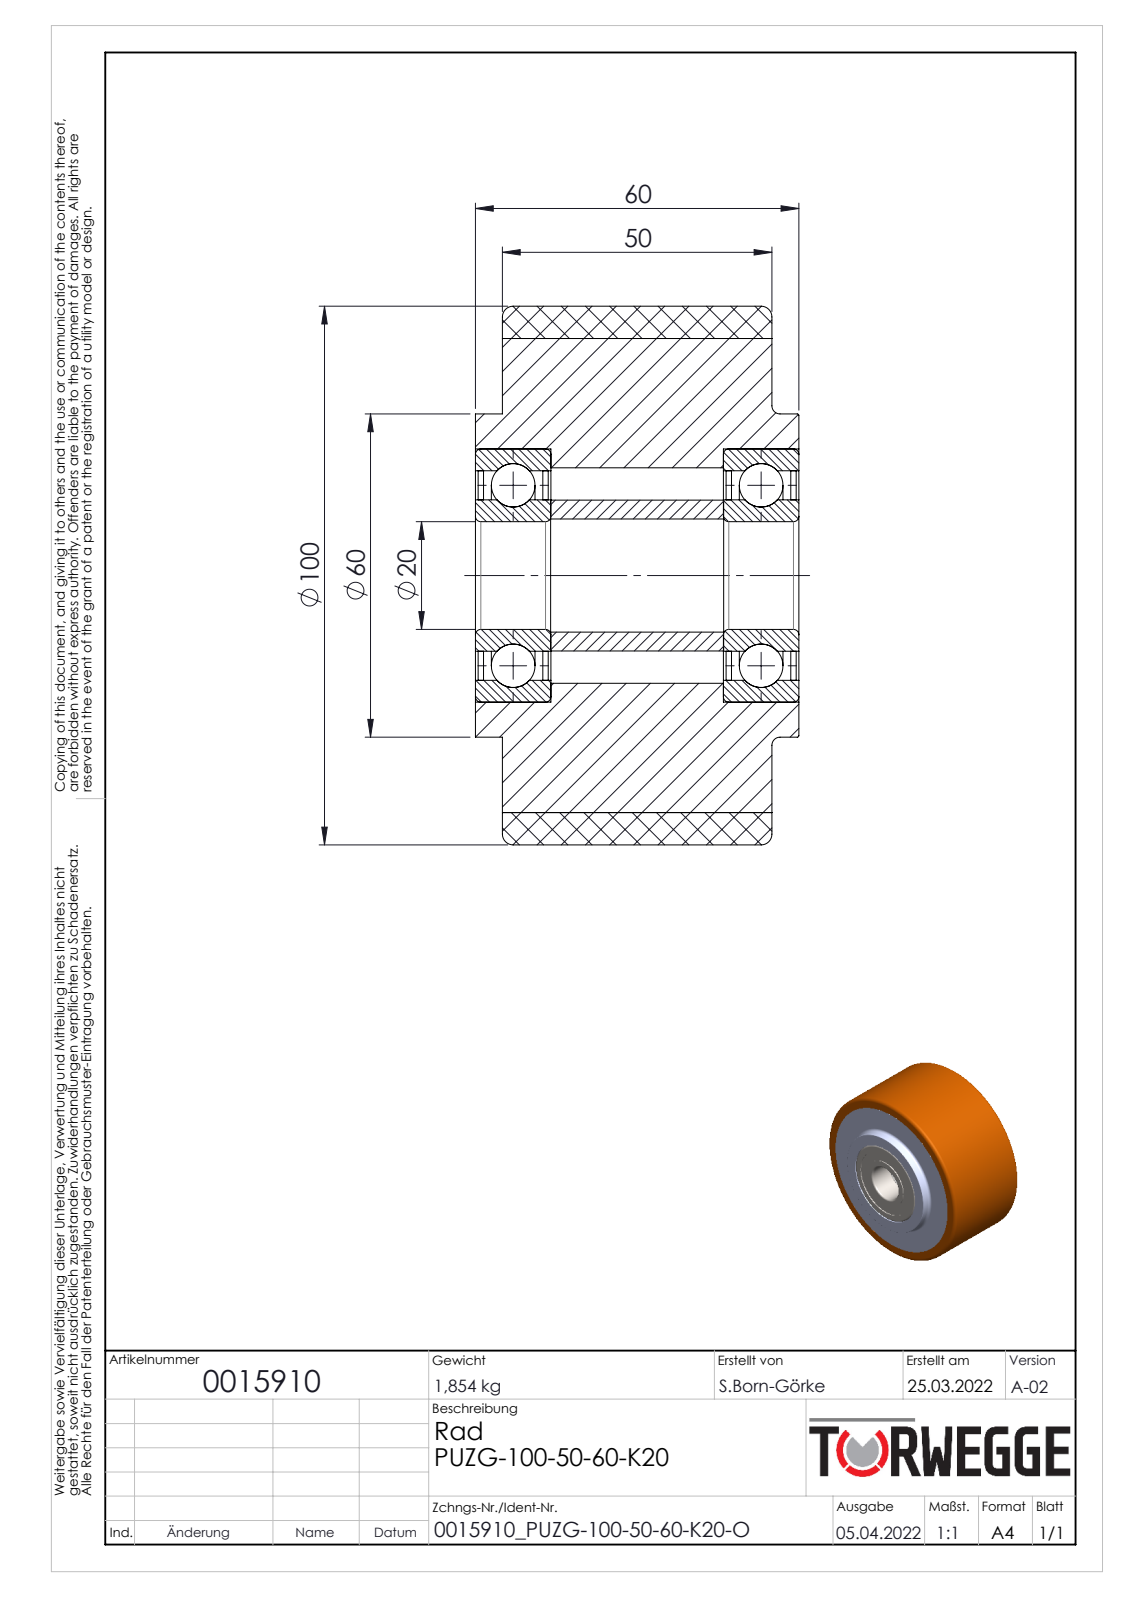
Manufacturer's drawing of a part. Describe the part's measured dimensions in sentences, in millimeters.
The part is named "0015910". Its 3-D file was written by "SolidWorks 2020 (AUTOMOTIVE_DESIGN)". It is 15 solids with 142 faces: 34 planar, 64 cylindrical and 44 other. Overall it measures 100 by 100 by 60 millimeters. Its volume is 374 887 cubic millimeters and its surface area 97 285 square millimeters. Round holes: 1 of diameter 20, 1 of diameter 21, 1 of diameter 28.1, 1 of diameter 38.9, 1 of diameter 40, 1 of diameter 47, 1 of diameter 88. Round bosses or shafts: 1 of diameter 100, 1 of diameter 60, 1 of diameter 28. Partial cylindrical surfaces (rounded edges, fillets, slot ends): 1 of radius 16.07, 1 of radius 17.43. The main face-to-face distances are 46, 50, 5, 55, 0.5, 1.5, 12.5, 13.5, 1, 12.
